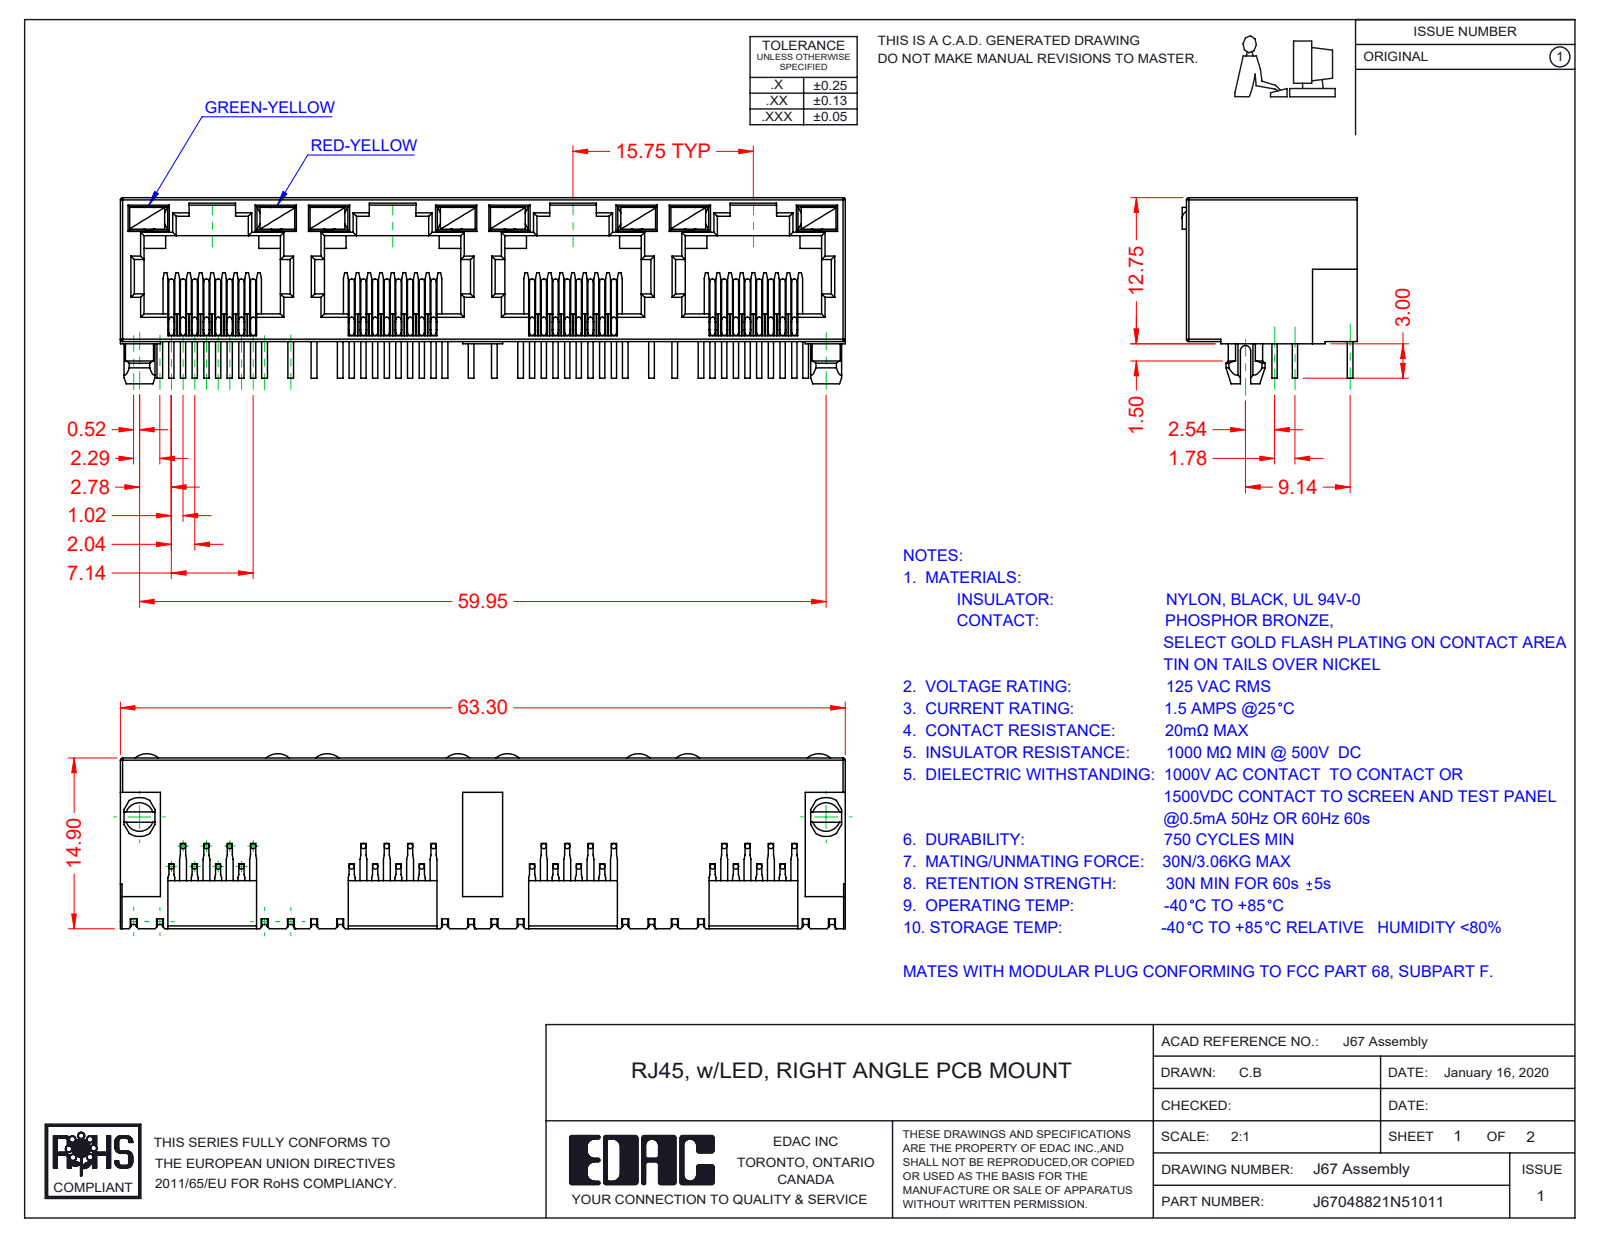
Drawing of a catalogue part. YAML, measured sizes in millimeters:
part_name: "67 LED RH_8-Red-Yellow; 67 Contacts; J67048822N58011; 67 LED LH_5-Green-Yellow (+1 more)"
step_written_by: "SolidWorks 2016 (CONFIG_CONTROL_DESIGN)"
units: millimeters
bodies: {solids: 41, faces: 2481, planar: 1781, cylindrical: 492, other: 208}
overall_size: [63.3, 16.25, 15.28]
volume: 5159
surface_area: 11573
round_bosses_or_shafts:
  - {diameter: 0.46, count: 96}
partial_cylinders:
  - {radius: 0.2, count: 66}
  - {radius: 0.3, count: 29}
  - {radius: 0.45, count: 9}
  - {radius: 1.55, count: 8}
  - {radius: 1.5, count: 2}
  - {radius: 1.7, count: 2}
  - {radius: 0.35, count: 1}
  - {radius: 1, count: 1}
face_to_face_distances: [0.5, 12.55, 1.89, 0.89, 10, 15.75, 1, 1.39, 11, 11.89]
